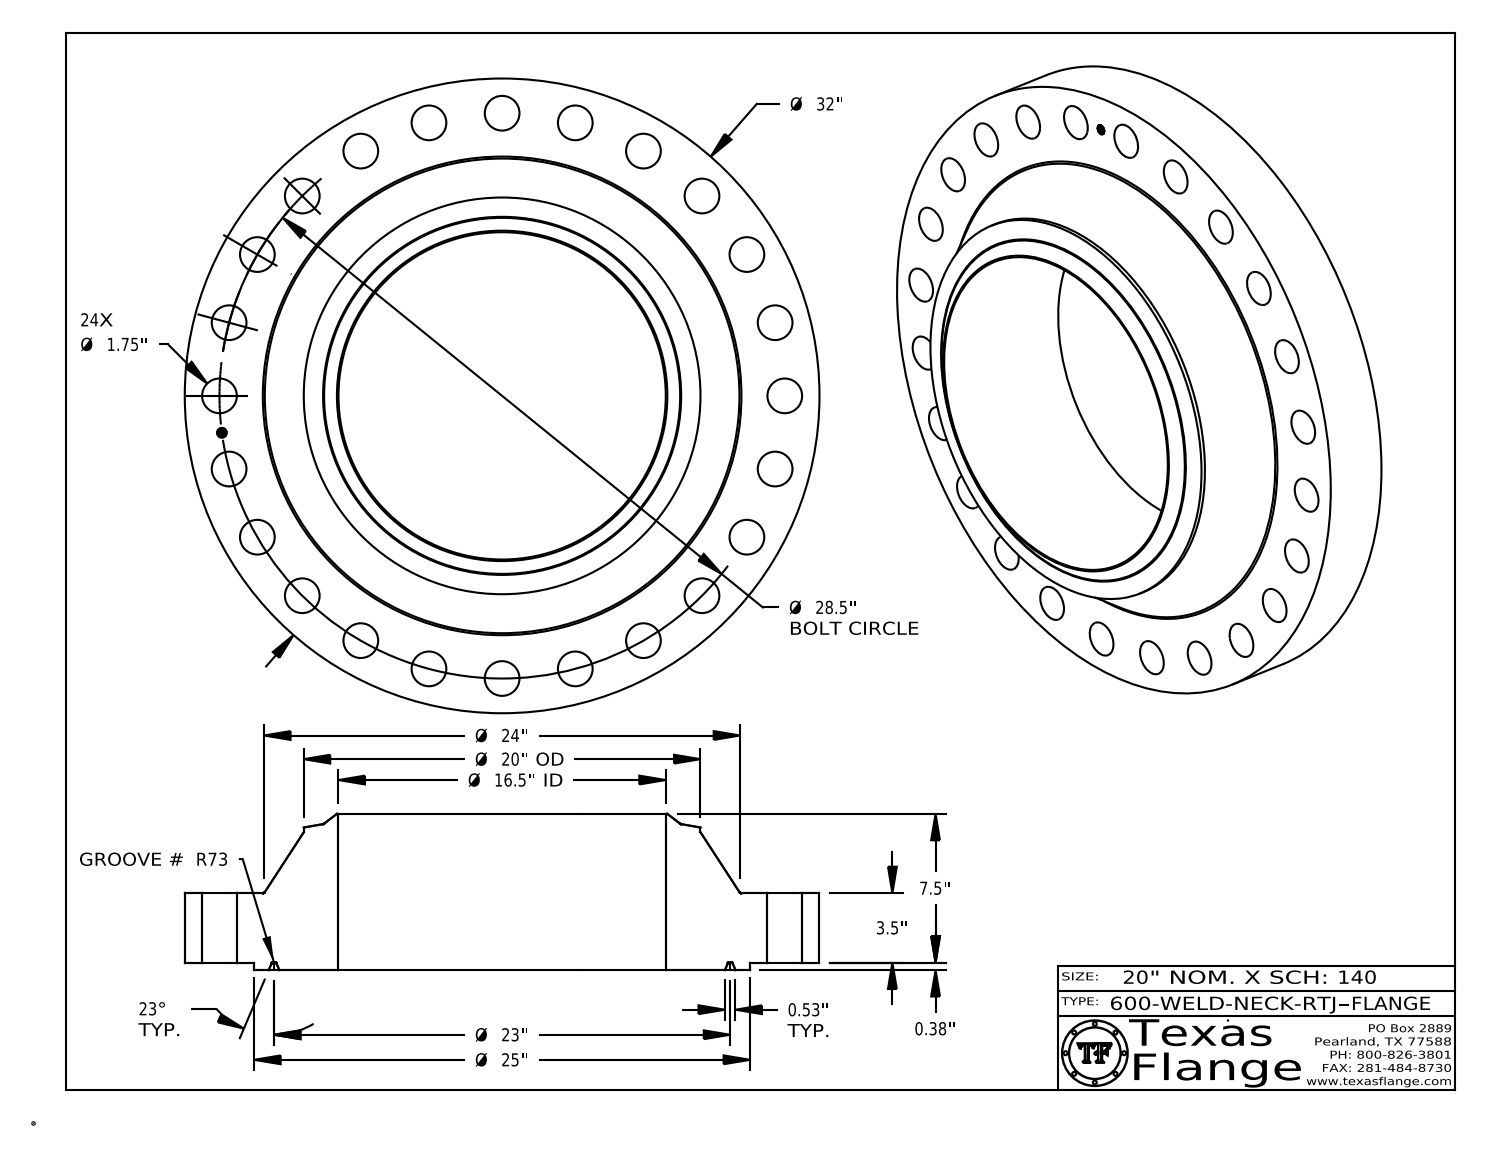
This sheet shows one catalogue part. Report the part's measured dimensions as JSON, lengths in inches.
{"part_name": "600-WELD-NECK-RTJ", "step_written_by": "CATIA V5 STEP AP214 (AUTOMOTIVE_DESIGN)", "units": "inches", "bodies": {"solids": 1, "faces": 465, "planar": 371, "cylindrical": 76, "other": 18}, "overall_size": [32, 32, 7.875], "volume_in3": 2520, "surface_area_in2": 2491, "round_holes": [[1.75, 24], [0.495, 1], [16.5, 1]], "round_bosses_or_shafts": [[0.03, 8], [32, 1], [25, 1], [20, 1], [0.39, 1]], "face_to_face_distances": [3.5, 0.375, 3.875, 7.875, 7.5, 4, 0.015, 3.86, 3.485, 4.015], "hole_center_spacings": [14.25, 3.72, 7.376, 24.682, 26.331, 27.529, 20.153, 10.907]}
